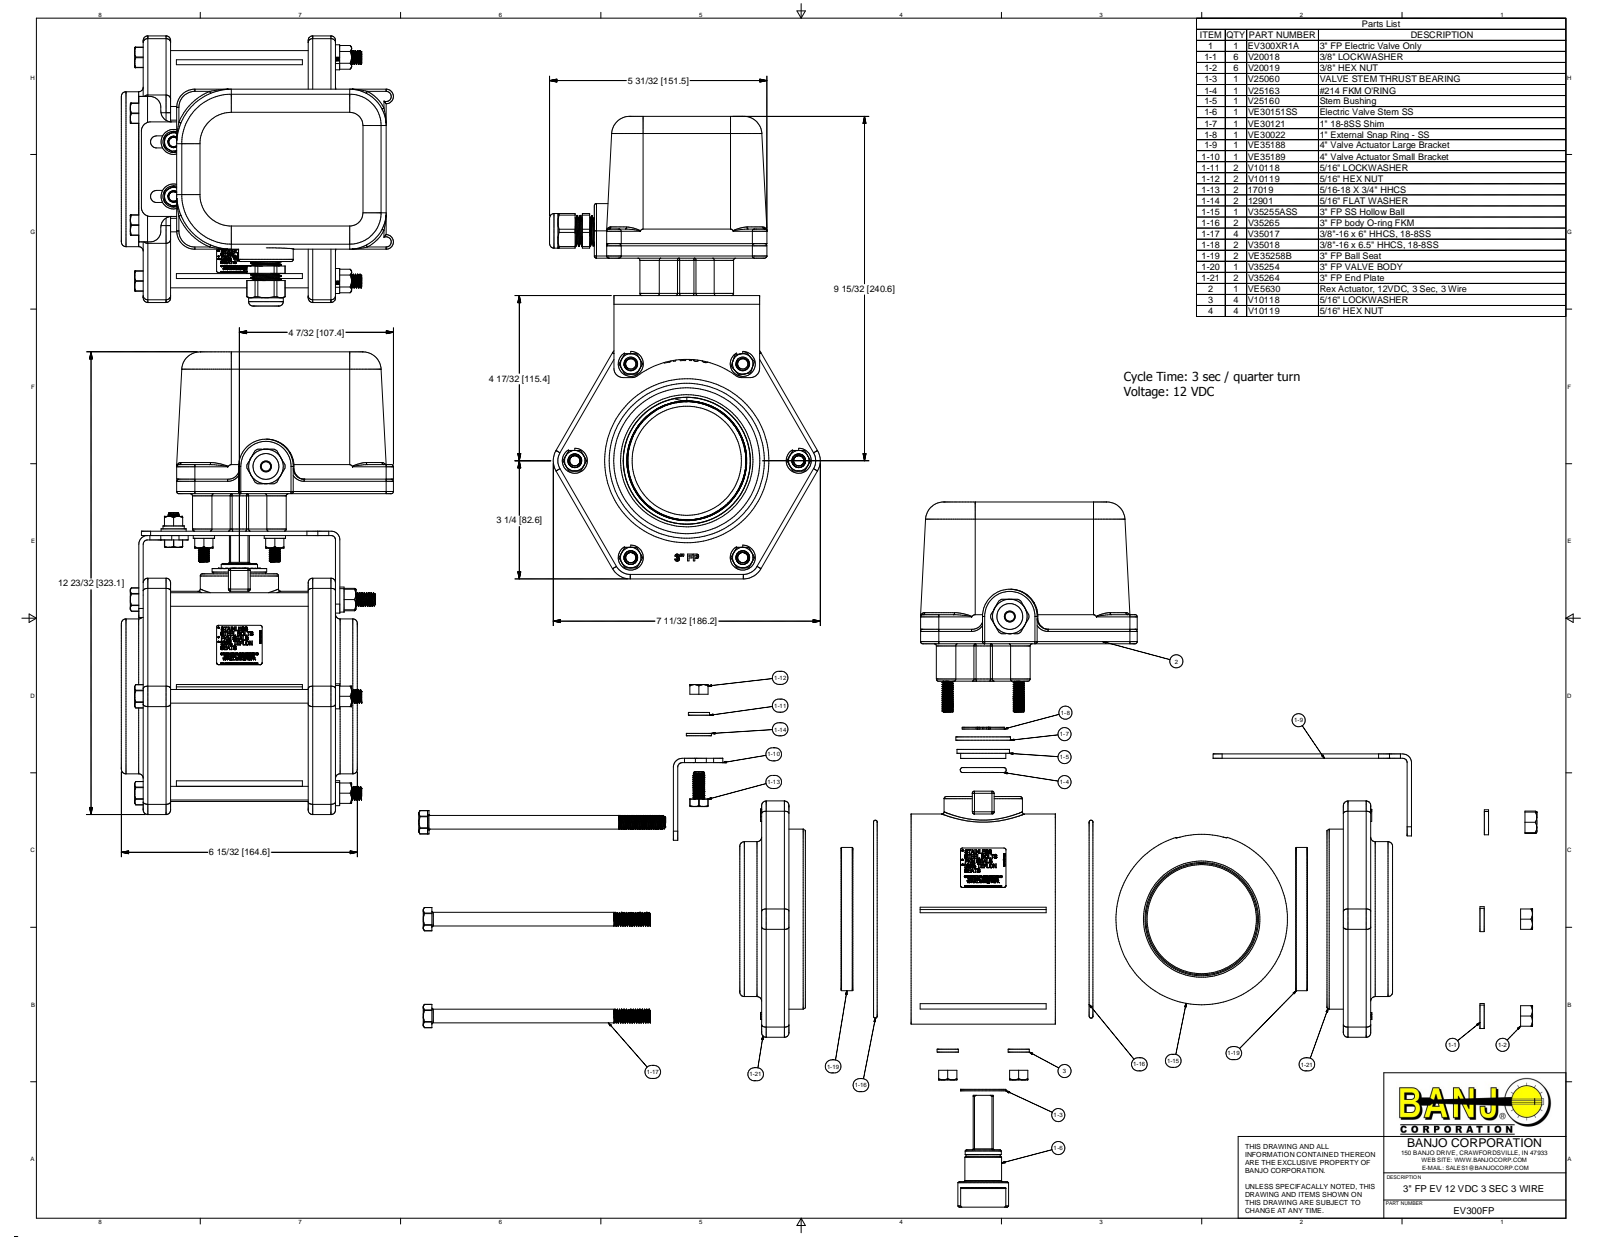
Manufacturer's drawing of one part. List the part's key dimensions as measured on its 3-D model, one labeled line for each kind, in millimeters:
Part name (STEP PRODUCT): V35254; VL1000; VX35264; V35264 (+8 more)
STEP written by: Autodesk Inventor 2016 (AUTOMOTIVE_DESIGN)
Units: millimetres
Bodies: 82 solids, 4583 faces (2005 planar, 923 cylindrical, 1655 other)
Overall size (bounding box): 323.15 × 189.74 × 188.74
Volume: 2 372 000 mm³ · Surface area: 700 798 mm²
Round holes (diameter × count): ⌀4.34 ×12, ⌀1.52 ×8, ⌀6.41 ×6, ⌀7.81 ×6, ⌀8.18 ×6, ⌀9.78 ×6, ⌀11.18 ×6, ⌀6.35 ×5, ⌀3.56 ×4, ⌀4.44 ×4, ⌀4.83 ×4, ⌀7.17 ×4
Round bosses / shafts (diameter × count): ⌀6.82 ×26, ⌀17.46 ×6, ⌀14.81 ×6, ⌀8 ×6, ⌀9.52 ×4, ⌀8.25 ×4, ⌀7.75 ×4, ⌀6.35 ×4
Partial cylindrical surfaces — rounded edges, fillets, slot ends (radius × count): R1.52 ×63, R3.17 ×24, R7.62 ×16, R0.76 ×14, R6.35 ×12, R4.38 ×8, R8.12 ×6, R12.7 ×6
Main face-to-face distances: 3.04, 134.12, 16.77, 117.35, 5.6, 18.67, 115.45, 1.9, 98.68, 68.58
Hole centre spacings: 71.24, 57.5, 137.62, 138, 20.65, 43.01, 118.55, 39.36
